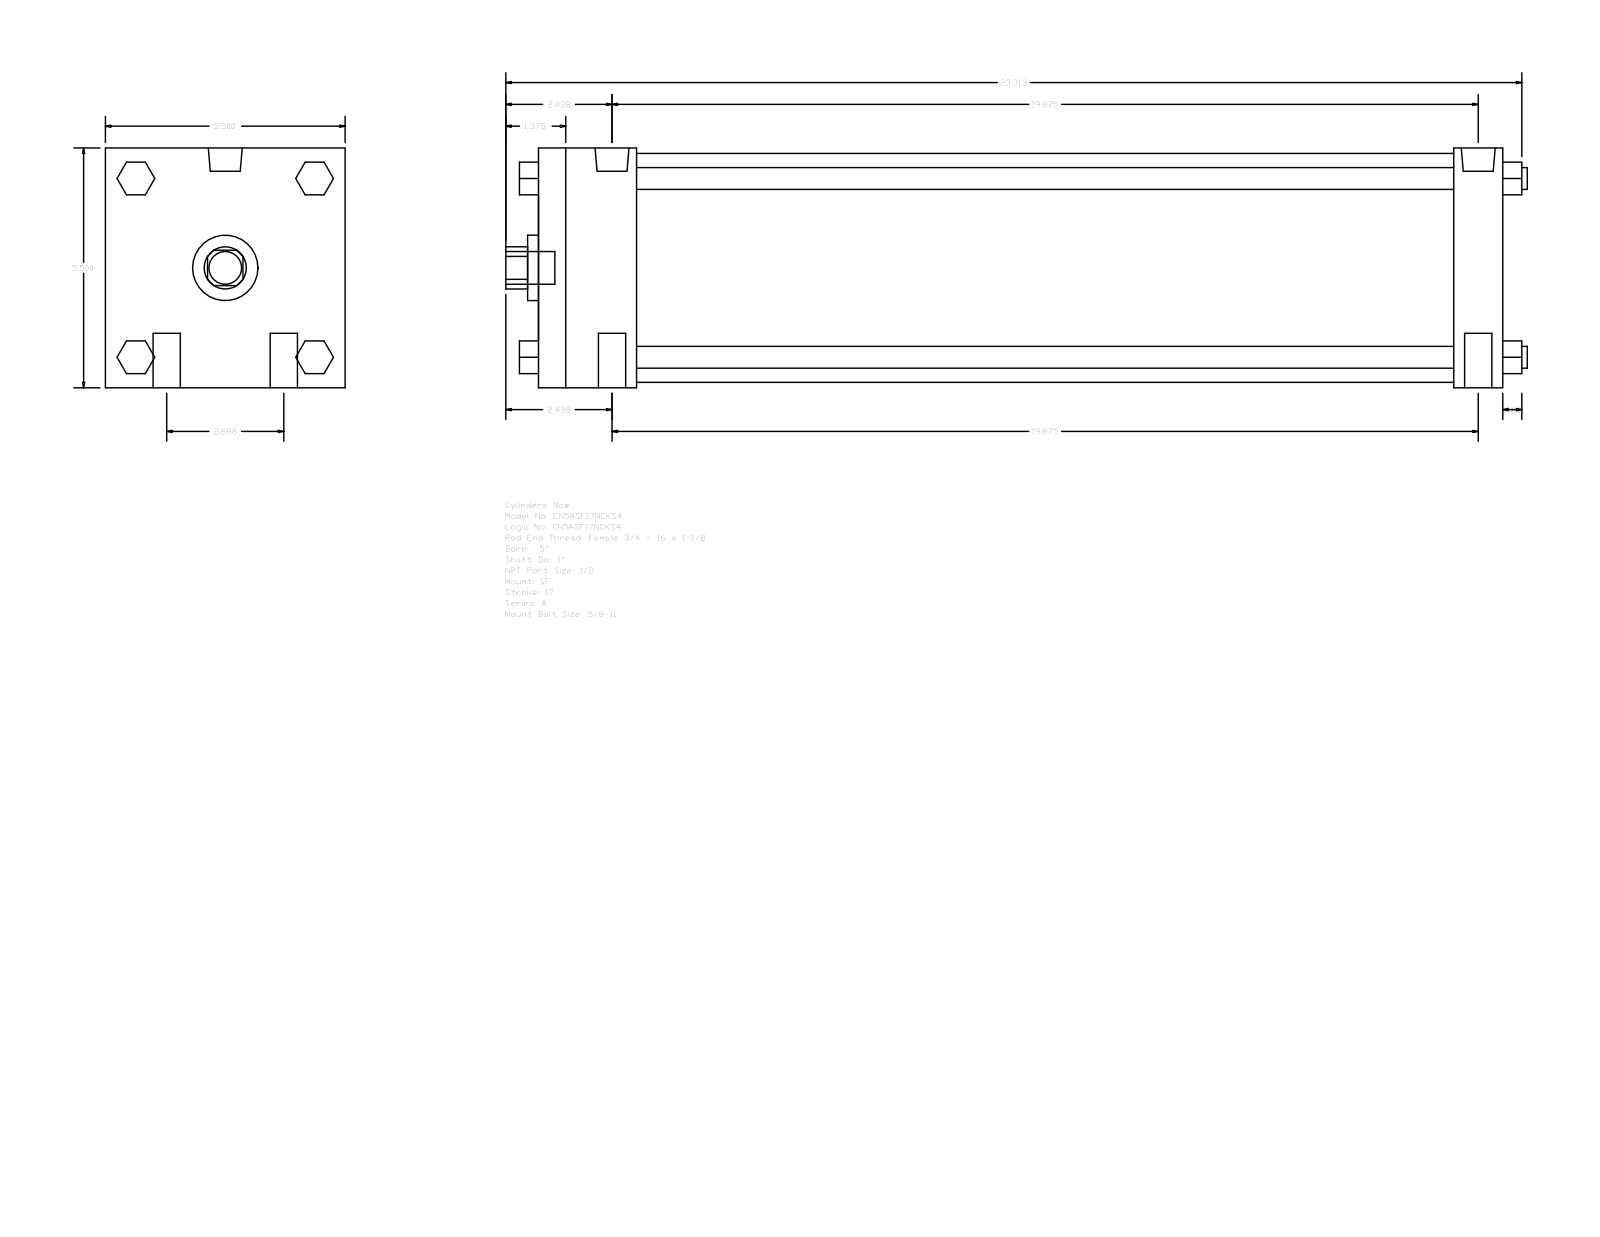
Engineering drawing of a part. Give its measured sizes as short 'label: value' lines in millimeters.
name: A_SF__0500_1
written by: GSSL Pune (CONFIG_CONTROL_DESIGN)
unit: mm
bodies: 0 solids, 124 faces (94 planar, 30 cylindrical, 0 other)
size: 595.31 × 139.7 × 139.7
holes: 1× ⌀25.4, 1× ⌀38.1, 1× ⌀133.35
bosses: 4× ⌀15.88, 4× ⌀12.7, 2× ⌀19.77, 2× ⌀8.73, 1× ⌀19.05
rounds: 1× R12.29
face distances: 139.7, 561.97, 28.57, 57.15, 533.4, 476.25, 504.82, 19.05, 52.07, 90.18
